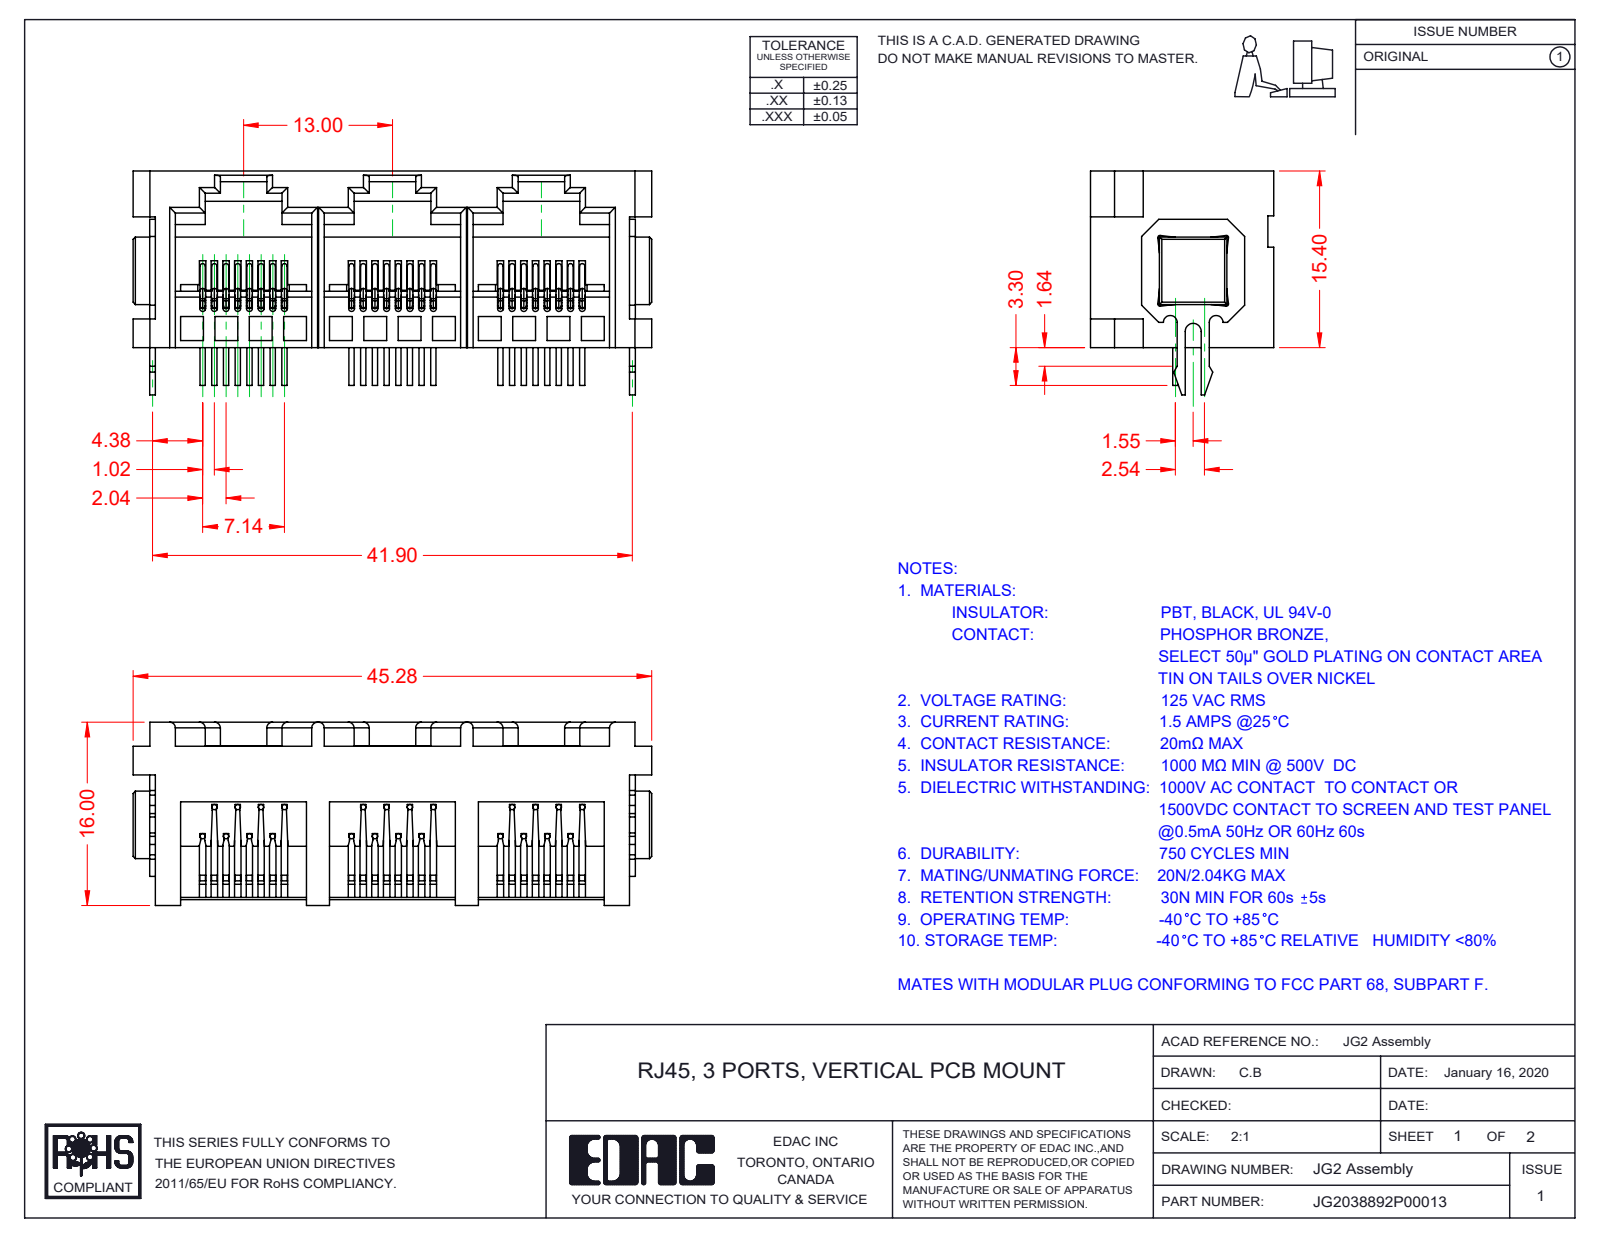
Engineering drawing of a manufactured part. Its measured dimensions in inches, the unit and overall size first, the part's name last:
Units: inches
Overall size (bounding box): 1.783 × 0.769 × 0.63
Round bosses / shafts (diameter × count): ⌀0.018 ×96
Partial cylindrical surfaces — rounded edges, fillets, slot ends (radius × count): R0.02 ×69, R0.008 ×4, R0.801 ×4, R0.012 ×3, R0.024 ×2, R0.008 ×1, R0.018 ×1, R0.028 ×1
Main face-to-face distances: 0.512, 0.472, 0.02, 0.134, 0.087, 0.436, 0.036, 1.024, 0.433, 0.079
Volume: 0.298 in³ · Surface area: 14.84 in²
Bodies: 30 solids, 1835 faces (1210 planar, 457 cylindrical, 168 other)
Part name (STEP PRODUCT): G2 Contacts; G2 Boardlock1; G2 Boardlock2; RJG2038892P00013 (+2 more)
STEP written by: SolidWorks 2016 (CONFIG_CONTROL_DESIGN)
